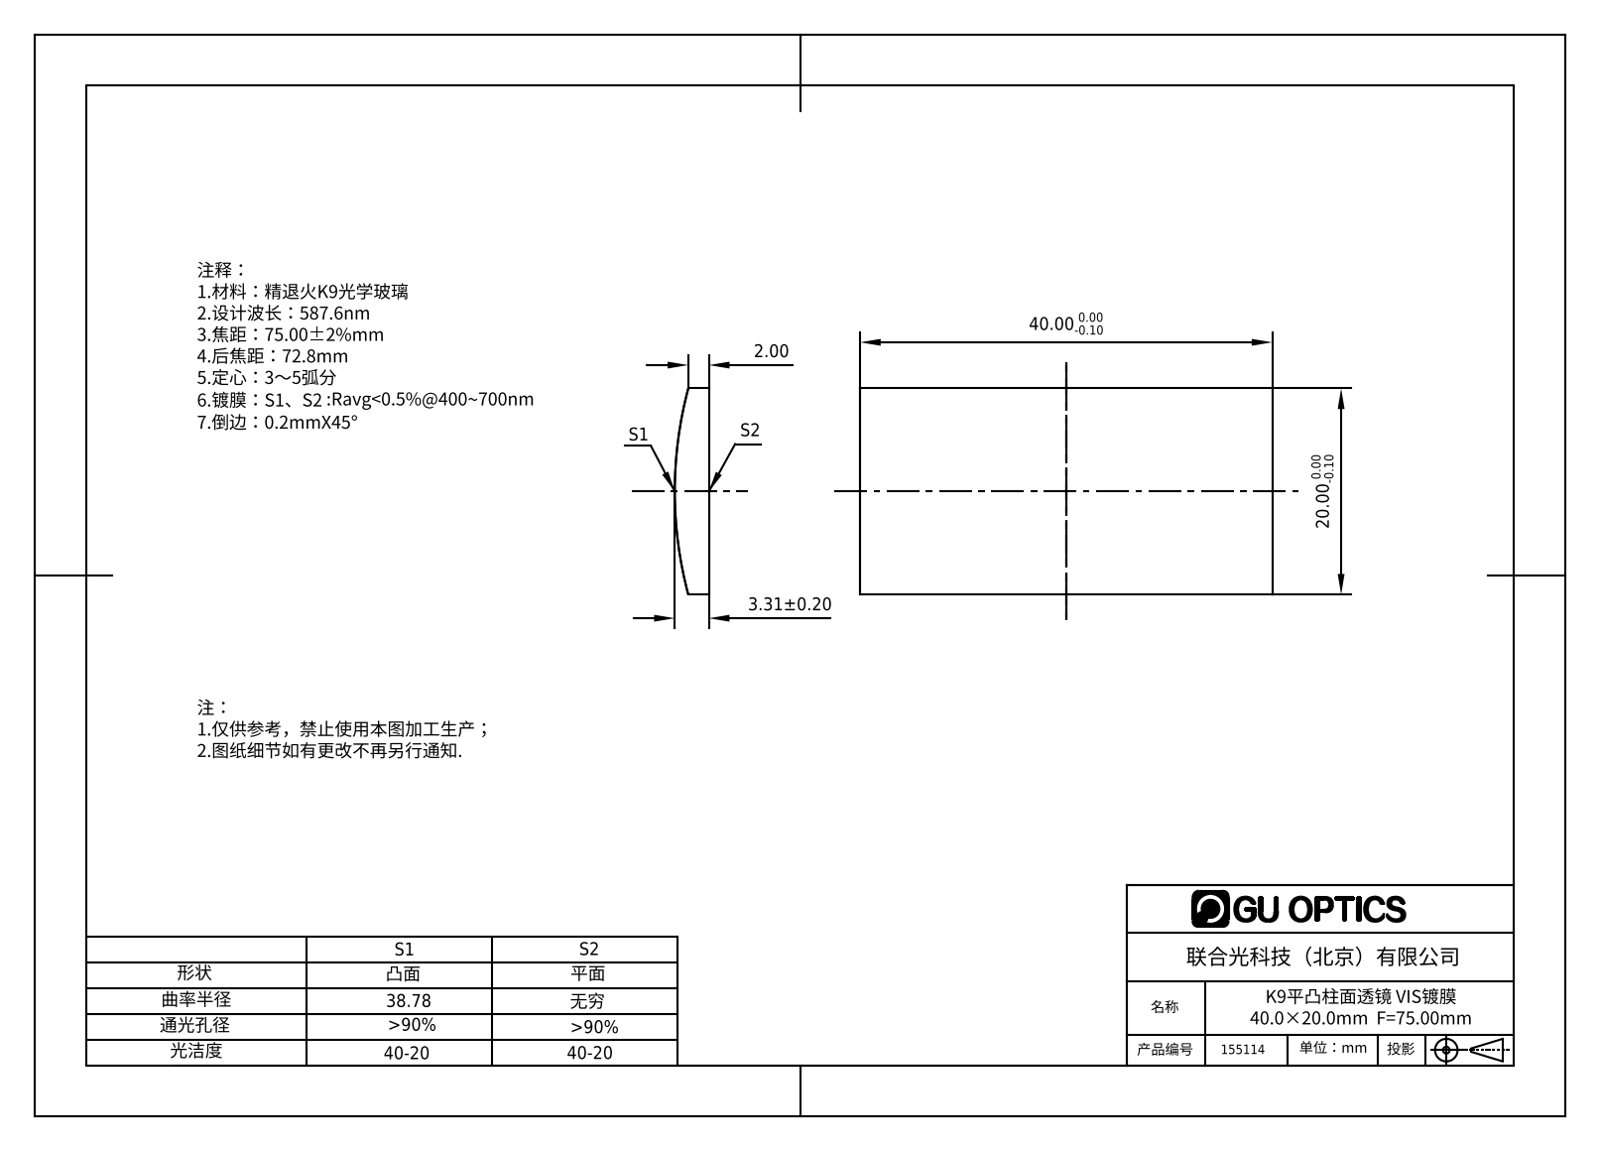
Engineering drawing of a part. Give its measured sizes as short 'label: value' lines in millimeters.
name: 155048
written by: SolidWorks 2016 (AUTOMOTIVE_DESIGN)
unit: mm
bodies: 1 solid, 6 faces (5 planar, 1 cylindrical, 0 other)
size: 40 × 20 × 3.31
volume: 2 301 mm³; area: 1 884 mm²
rounds: 1× R38.78
face distances: 20, 40
